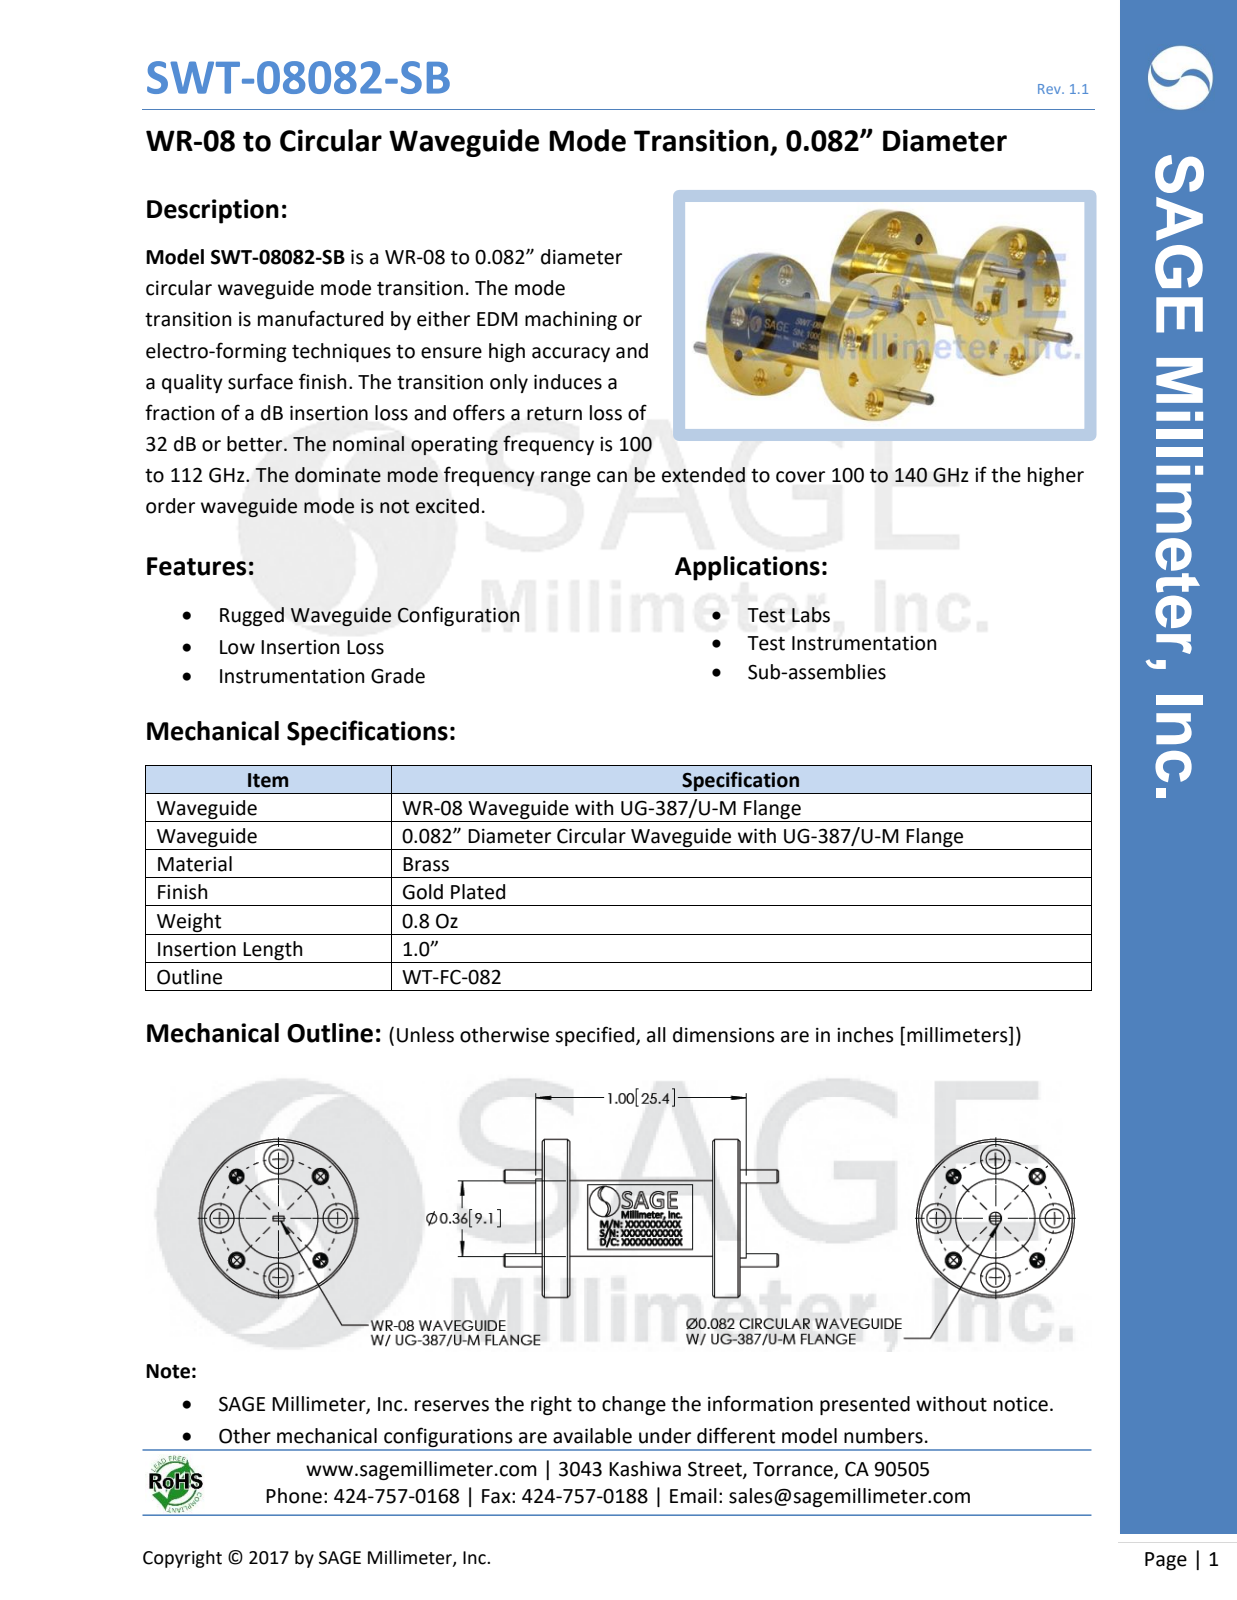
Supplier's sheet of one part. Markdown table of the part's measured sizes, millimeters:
| quantity | value |
| --- | --- |
| part name | SWT-08082-SB |
| STEP written by | SolidWorks 2016 (CONFIG_CONTROL_DESIGN) |
| units | millimeters |
| bodies | 5 solids, 138 faces (24 planar, 66 cylindrical, 48 other) |
| overall size | 33.1 × 19.1 × 19.1 |
| volume | 3 000 mm³ |
| surface area | 2 321 mm² |
| round holes (diameter × count) | 1.5 × 4, 1.7 × 4, 2.3 × 4, 3.6 × 4 |
| round bosses / shafts (diameter × count) | 1.6 × 4, 19.1 × 1, 9.5 × 1, 9.1 × 1 |
| main face-to-face distances | 17.3, 3.3, 20.6, 23.9, 20.6, 3.3, 0.8, 24.6, 21.3, 4.1 |
| hole center spacings | 5.5, 13.2, 10.1, 14.3, 10.1, 5.5, 13.2, 13.2 |
